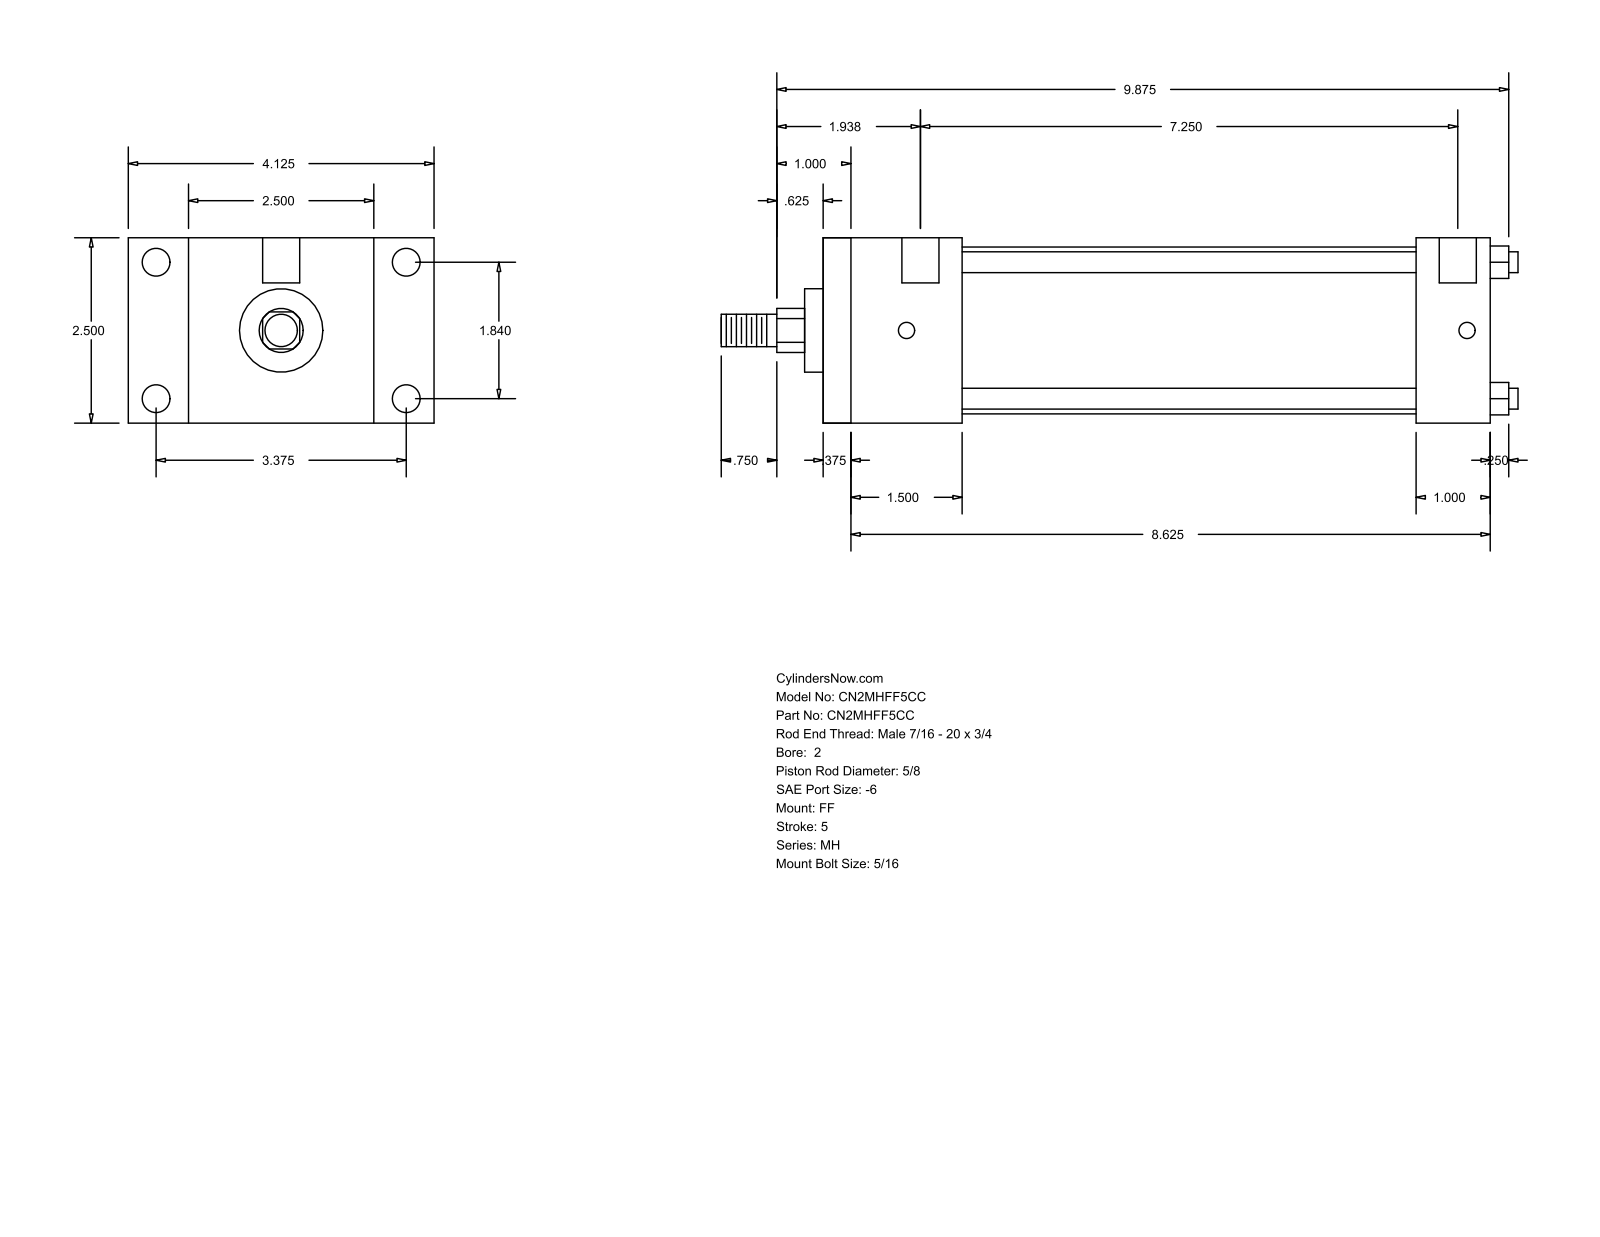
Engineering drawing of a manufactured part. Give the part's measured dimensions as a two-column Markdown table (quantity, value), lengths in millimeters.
| quantity | value |
| --- | --- |
| part name | MH_FF__0200_0.625 |
| STEP written by | GSSL Pune (CONFIG_CONTROL_DESIGN) |
| units | millimeters |
| bodies | 0 solids, 92 faces (64 planar, 28 cylindrical, 0 other) |
| overall size | 273.05 × 104.78 × 63.5 |
| round holes (diameter × count) | 5.56 × 4, 9.53 × 4, 12.7 × 2 |
| round bosses / shafts (diameter × count) | 7.14 × 4, 57.15 × 1, 28.57 × 1, 15.88 × 1, 11.11 × 1 |
| partial cylindrical surfaces (radius × count) | 7.54 × 1 |
| main face-to-face distances | 63.5, 228.59, 219.07, 9.52, 25.4, 38.1, 47.62, 203.19, 193.67, 155.57 |
| hole center spacings | 46.74, 85.72, 97.63, 192.09, 3.18, 4.76, 184.15, 187.33 |
